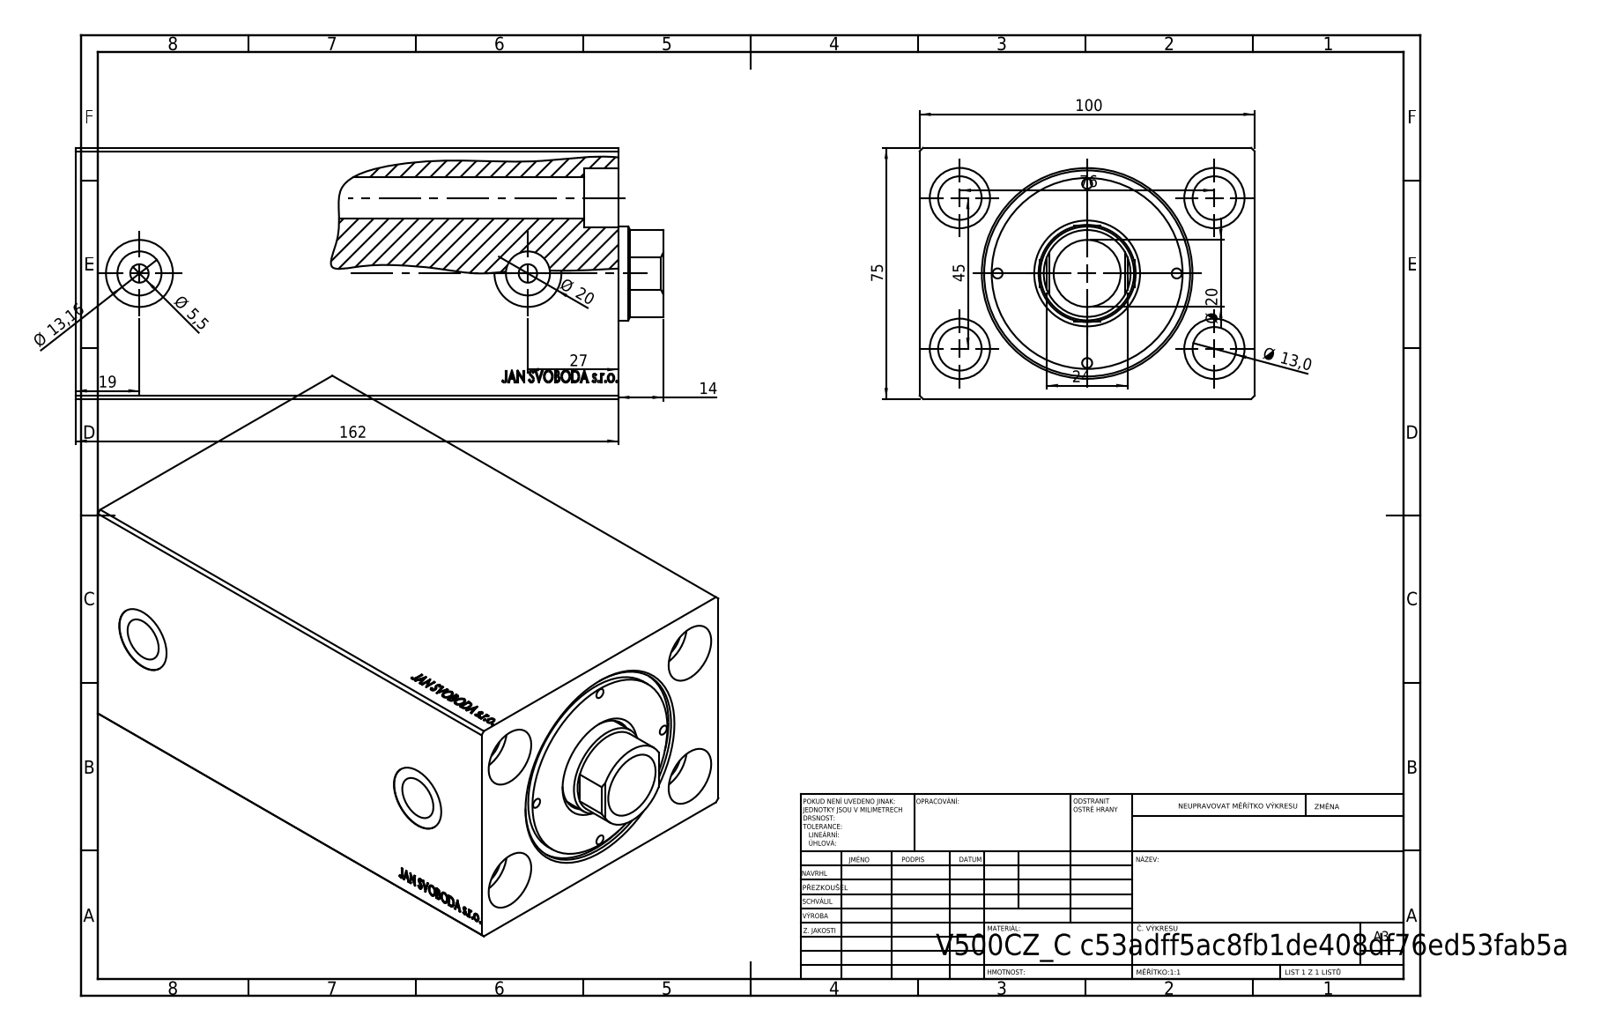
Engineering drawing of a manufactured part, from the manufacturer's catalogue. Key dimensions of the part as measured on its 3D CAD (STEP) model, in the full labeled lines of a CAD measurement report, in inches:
Part name (STEP PRODUCT): V500CZ_C; V500CZ_VC_vysunovaci_C; V500CZ_VCP_C
STEP written by: SolidWorks 2019 (CONFIG_CONTROL_DESIGN)
Units: inches
Bodies: 3 solids, 888 faces (415 planar, 79 cylindrical, 394 other)
Overall size (bounding box): 6.909 × 3.937 × 2.953
Volume: 61.39 in³ · Surface area: 225.7 in²
Round holes (diameter × count): ⌀0.118 ×4, ⌀0.512 ×4, ⌀0.709 ×4, ⌀0.787 ×3, ⌀0.217 ×2, ⌀0.518 ×2, ⌀0.535 ×2, ⌀1.102 ×1, ⌀1.142 ×1, ⌀1.417 ×1, ⌀1.969 ×1, ⌀2.421 ×1
Round bosses / shafts (diameter × count): ⌀2.244 ×1
Partial cylindrical surfaces — rounded edges, fillets, slot ends (radius × count): R0.51 ×1
Main face-to-face distances: 2.953, 3.937, 6.378, 4.528, 1.85, 0.465, 4.063, 5.913, 0.394, 0.071
Hole centre spacings: 0.991, 1.053, 1.489, 1.506, 1.739, 2.449, 2.699, 1.772
